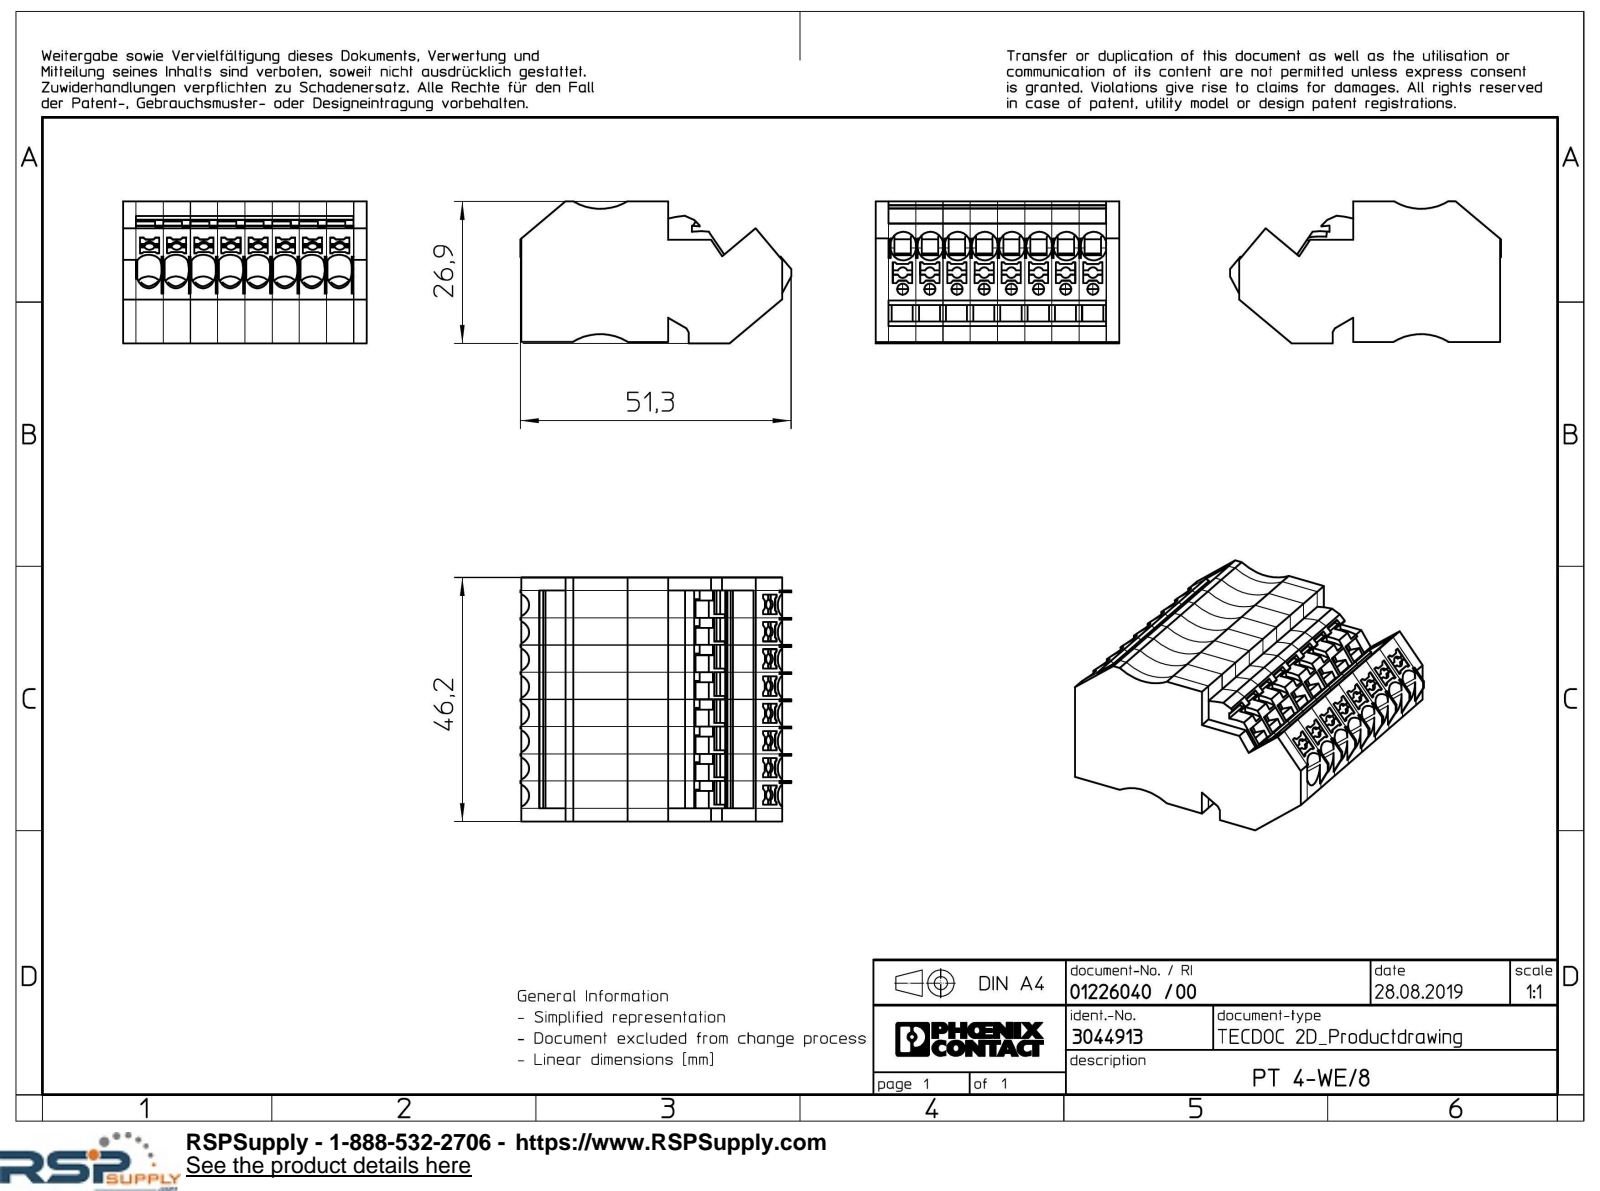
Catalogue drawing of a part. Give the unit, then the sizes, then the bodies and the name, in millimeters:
Units: millimetres
Overall size (bounding box): 51.3 × 46.2 × 26.9
Round holes (diameter × count): ⌀2.1 ×8
Partial cylindrical surfaces — rounded edges, fillets, slot ends (radius × count): R2.4 ×32, R1 ×16, R1.03 ×3, R10 ×2, R1.05 ×1, R1.78 ×1, R12.4 ×1, R13.38 ×1
Main face-to-face distances: 46.2, 5.15, 10.3, 15.45, 7.2, 3.15, 3.85, 7, 27.8, 20.6
Hole centre spacings: 5.15, 10.3, 15.45, 20.6, 25.75, 30.9, 36.05
Volume: 41 946 mm³ · Surface area: 16 650 mm²
Bodies: 1 solid, 1363 faces (1183 planar, 164 cylindrical, 16 other)
Part name (STEP PRODUCT): PT_4_WE_8-select
STEP written by: Creo Elements/Direct Modeling 20.1A 29-Sep-2018 (C) Parametric Technology GmbH (AUTOMOTIVE_DESIGN)
